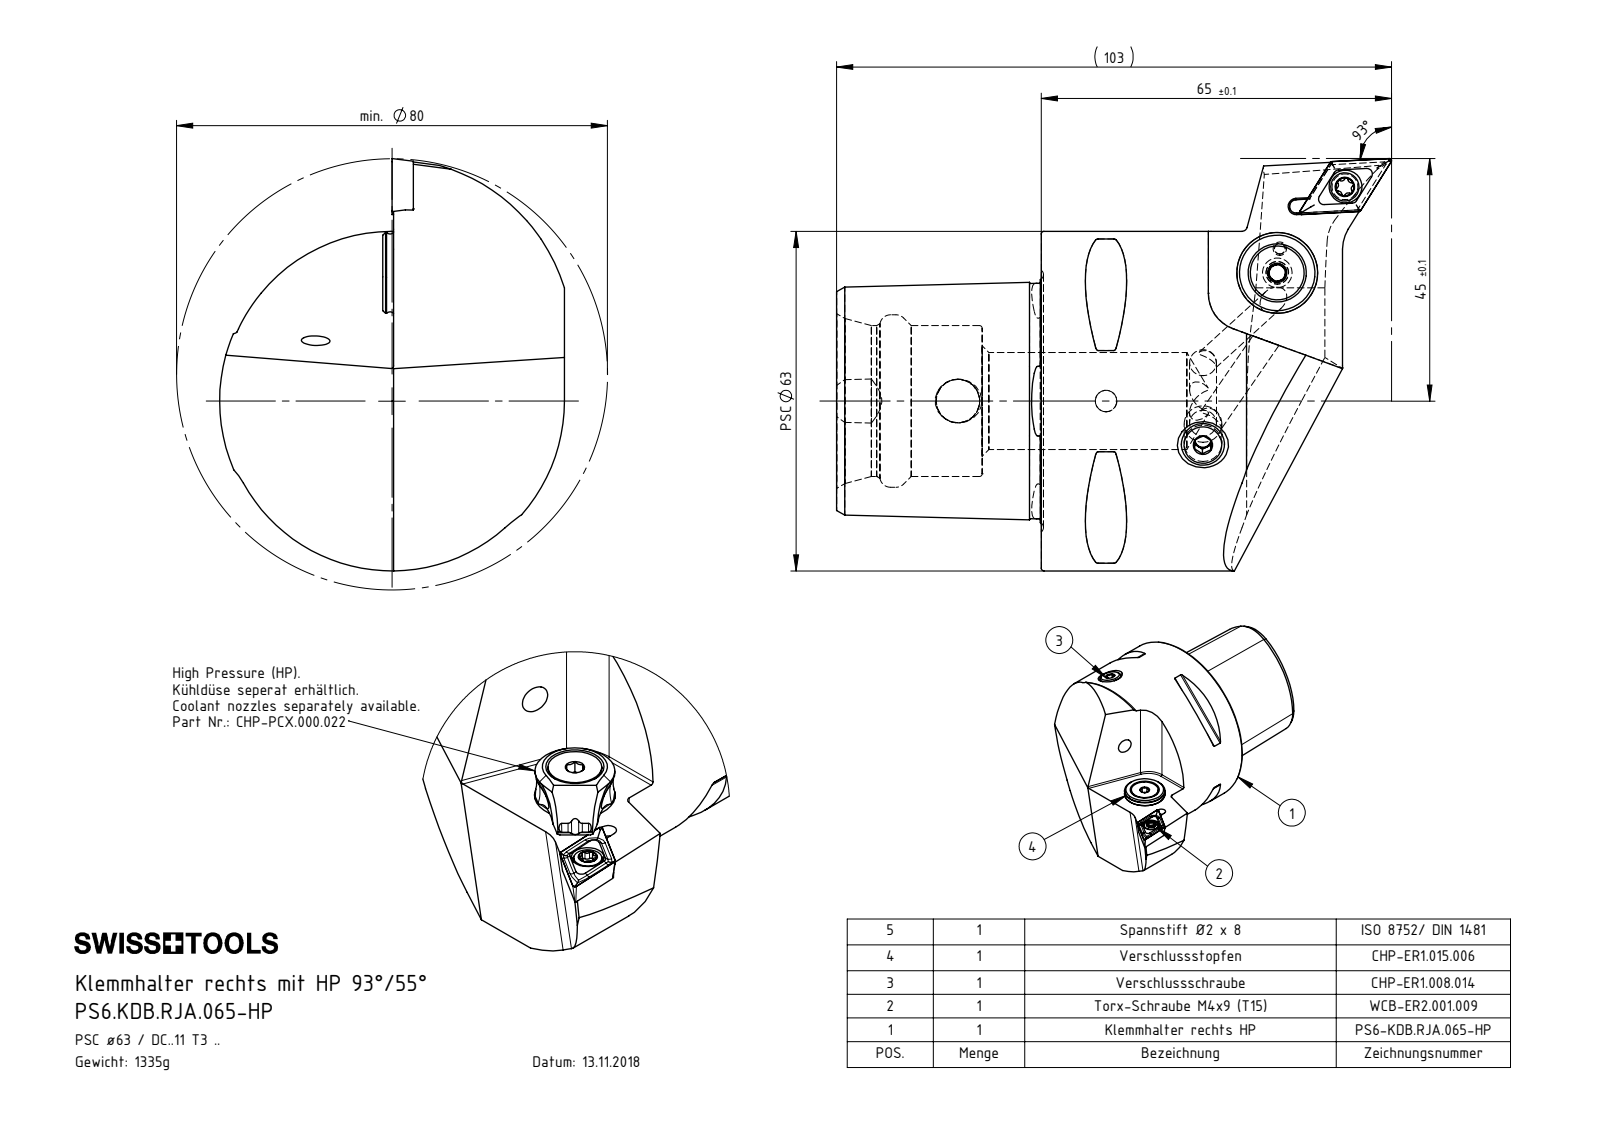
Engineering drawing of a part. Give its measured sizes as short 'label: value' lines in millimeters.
name: CHP-ER1.008.014_A; CHP-ER1.015.006; CHP-ER1.015.006_A; DCMT11T304 (+6 more)
written by: SolidWorks 2017 (AUTOMOTIVE_DESIGN)
unit: mm
bodies: 8 solids, 376 faces (91 planar, 99 cylindrical, 186 other)
size: 103.01 × 76.5 × 64
volume: 170 138 mm³; area: 31 323 mm²
holes: 2× ⌀4.2, 2× ⌀5, 1× ⌀1.2, 1× ⌀2, 1× ⌀2.5, 1× ⌀3, 1× ⌀3.3, 1× ⌀4, 1× ⌀4.4, 1× ⌀5.2, 1× ⌀6.1, 1× ⌀7
bosses: 1× ⌀63, 1× ⌀15, 1× ⌀13.4, 1× ⌀10, 1× ⌀8, 1× ⌀5.5, 1× ⌀5.25, 1× ⌀5
rounds: 10× R0.5, 6× R0.34, 6× R0.59, 2× R7, 1× R1.25, 1× R6, 1× R32, 1× R34
face distances: 38, 24.88, 31.7, 27.2, 4.5, 27, 11, 69, 42, 31
hole spacings: 4.49, 16.67, 16.79, 20.3, 20.42, 27.5, 39.71, 42.89
